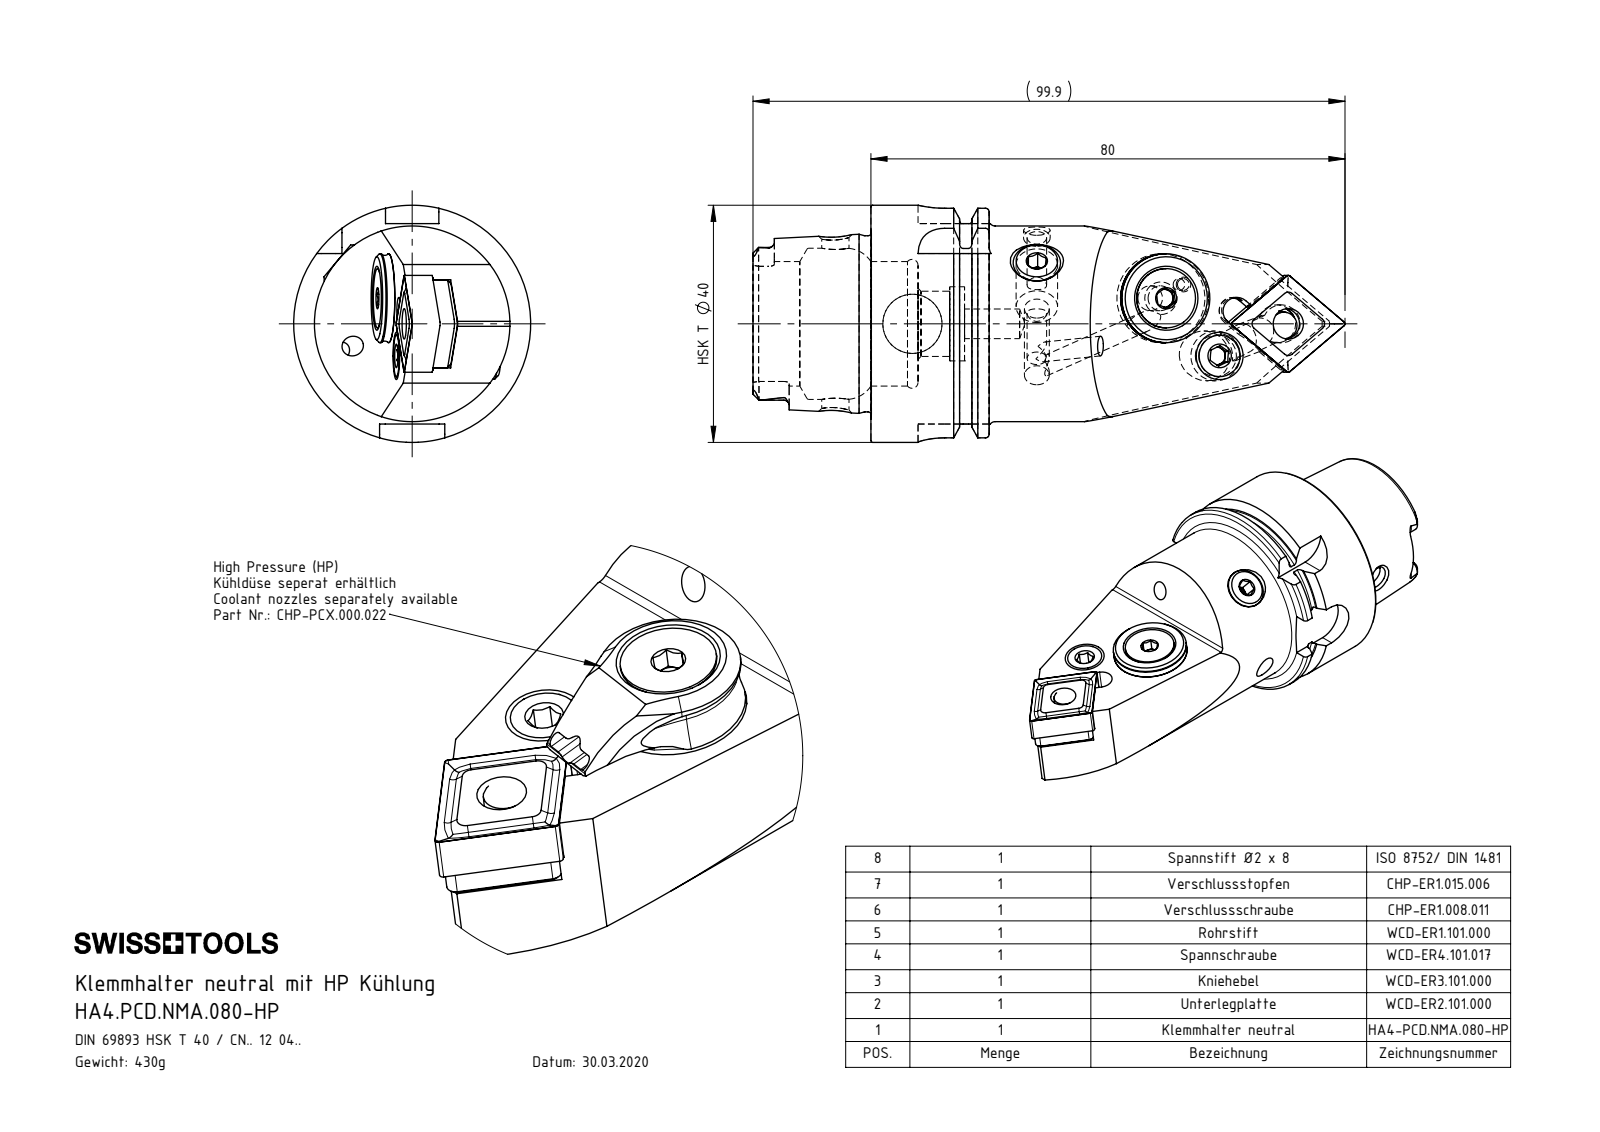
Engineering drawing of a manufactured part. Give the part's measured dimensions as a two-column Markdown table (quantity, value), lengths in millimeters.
| quantity | value |
| --- | --- |
| part name | CHP-PCX.000.022_B; CNMG120404; DIN 3771 - 6.5x1.5; ISO 4026 - M5 x 5 (+8 more) |
| STEP written by | SolidWorks 2022 (AUTOMOTIVE_DESIGN) |
| units | millimeters |
| bodies | 13 solids, 473 faces (180 planar, 118 cylindrical, 175 other) |
| overall size | 99.9 × 40 × 40 |
| volume | 54 072 mm³ |
| surface area | 20 768 mm² |
| round holes (diameter × count) | 4.2 × 4, 5.3 × 2, 7 × 2, 1.2 × 1, 2 × 1, 3 × 1, 3.3 × 1, 4.6 × 1, 5 × 1, 5.16 × 1, 6.55 × 1, 8.4 × 1 |
| round bosses / shafts (diameter × count) | 8 × 2, 5 × 2, 40 × 1, 34.75 × 1, 33 × 1, 29.71 × 1, 14.85 × 1, 13.4 × 1 |
| partial cylindrical surfaces (radius × count) | 1 × 11, 0.9 × 6, 0.4 × 4, 1.88 × 4, 4.5 × 4, 6 × 3, 0.5 × 2, 1.1 × 2 |
| main face-to-face distances | 4.47, 7.95, 19.95, 12, 4.5, 3, 19.9, 27.85, 39.85, 1.5 |
| hole center spacings | 4.49, 4.5, 13.25, 18.5, 12.86, 12.93, 13.5, 13.51 |
